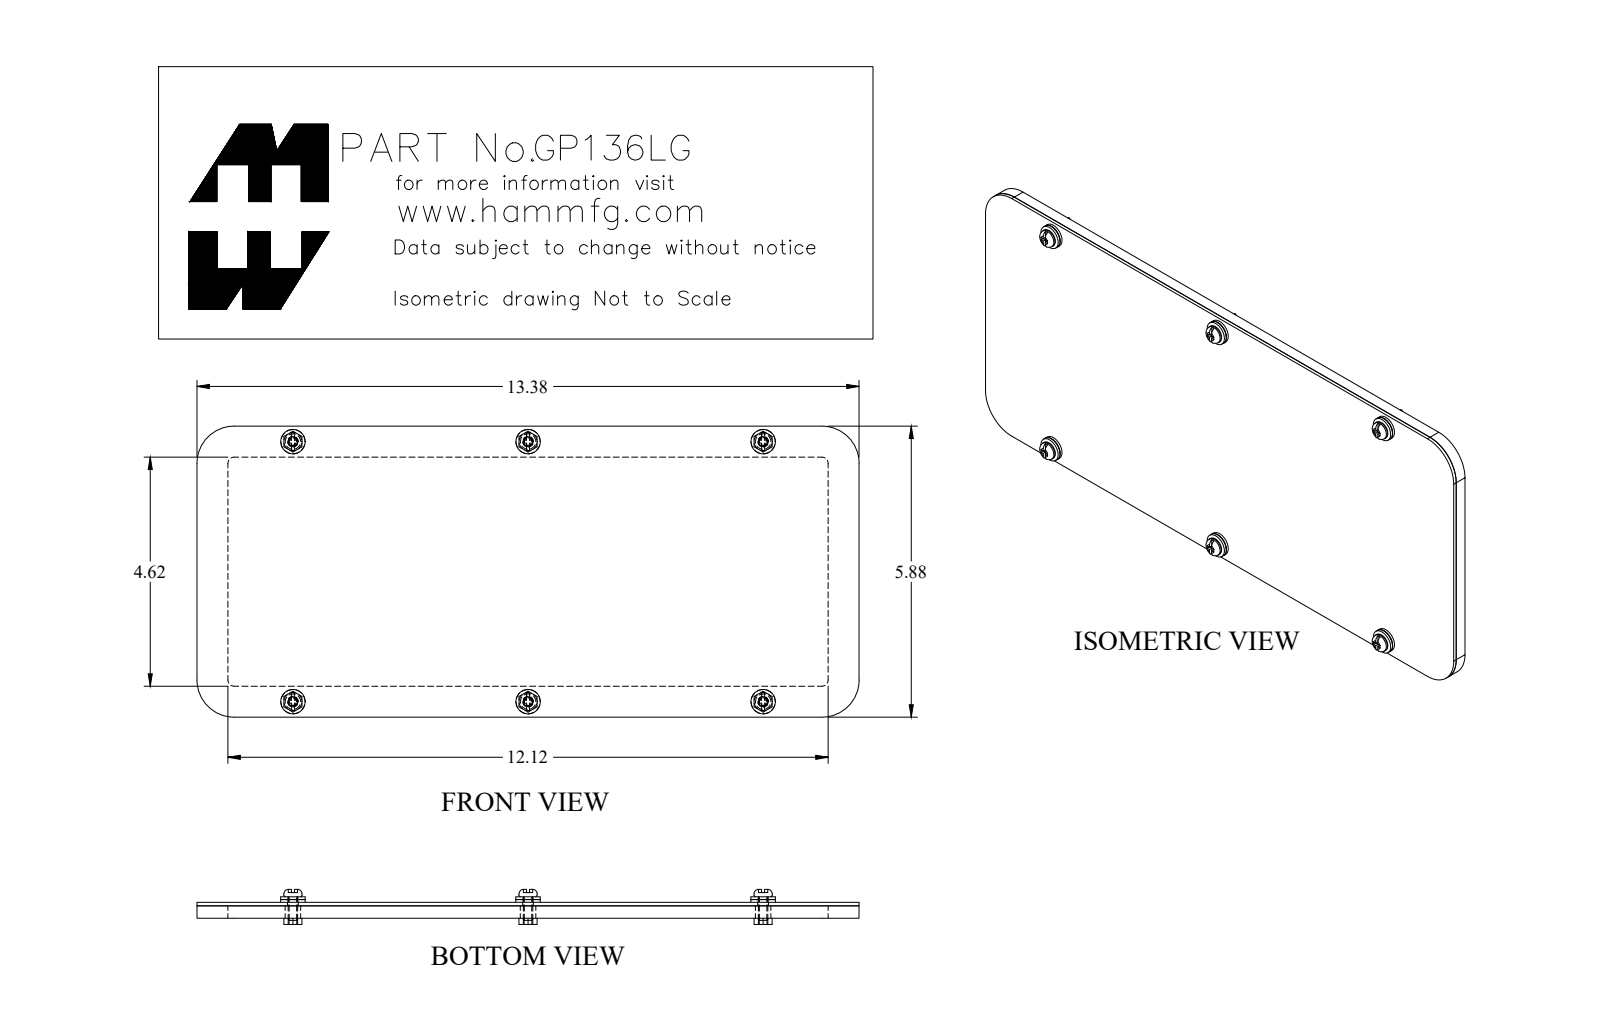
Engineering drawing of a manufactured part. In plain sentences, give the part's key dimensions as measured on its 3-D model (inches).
The part is named "GP136LG". Its 3-D file was written by "SolidWorks 2018 (AUTOMOTIVE_DESIGN)". It is 20 solids with 346 faces: 190 planar, 120 cylindrical and 36 other. Overall it measures 13.375 by 5.875 by 0.707 inches. Its volume is 11.33 cubic inches and its surface area 230.8 square inches. Round holes: 6 of diameter 0.156, 6 of diameter 0.197, 6 of diameter 0.218, 6 of diameter 0.313. Round bosses or shafts: 6 of diameter 0.494, 6 of diameter 0.488, 6 of diameter 0.367, 6 of diameter 0.19. Partial cylindrical surfaces (rounded edges, fillets, slot ends): 4 of radius 0.125, 4 of radius 0.75. The main face-to-face distances are 0.072, 0.322, 0.25, 0.625, 5.25, 5.875, 4.625, 12.75, 13.375, 0.11. The hole center spacings are 4.75, 7.08, 9.499, 5.25, 7.08, 7.08, 10.854, 4.749.
